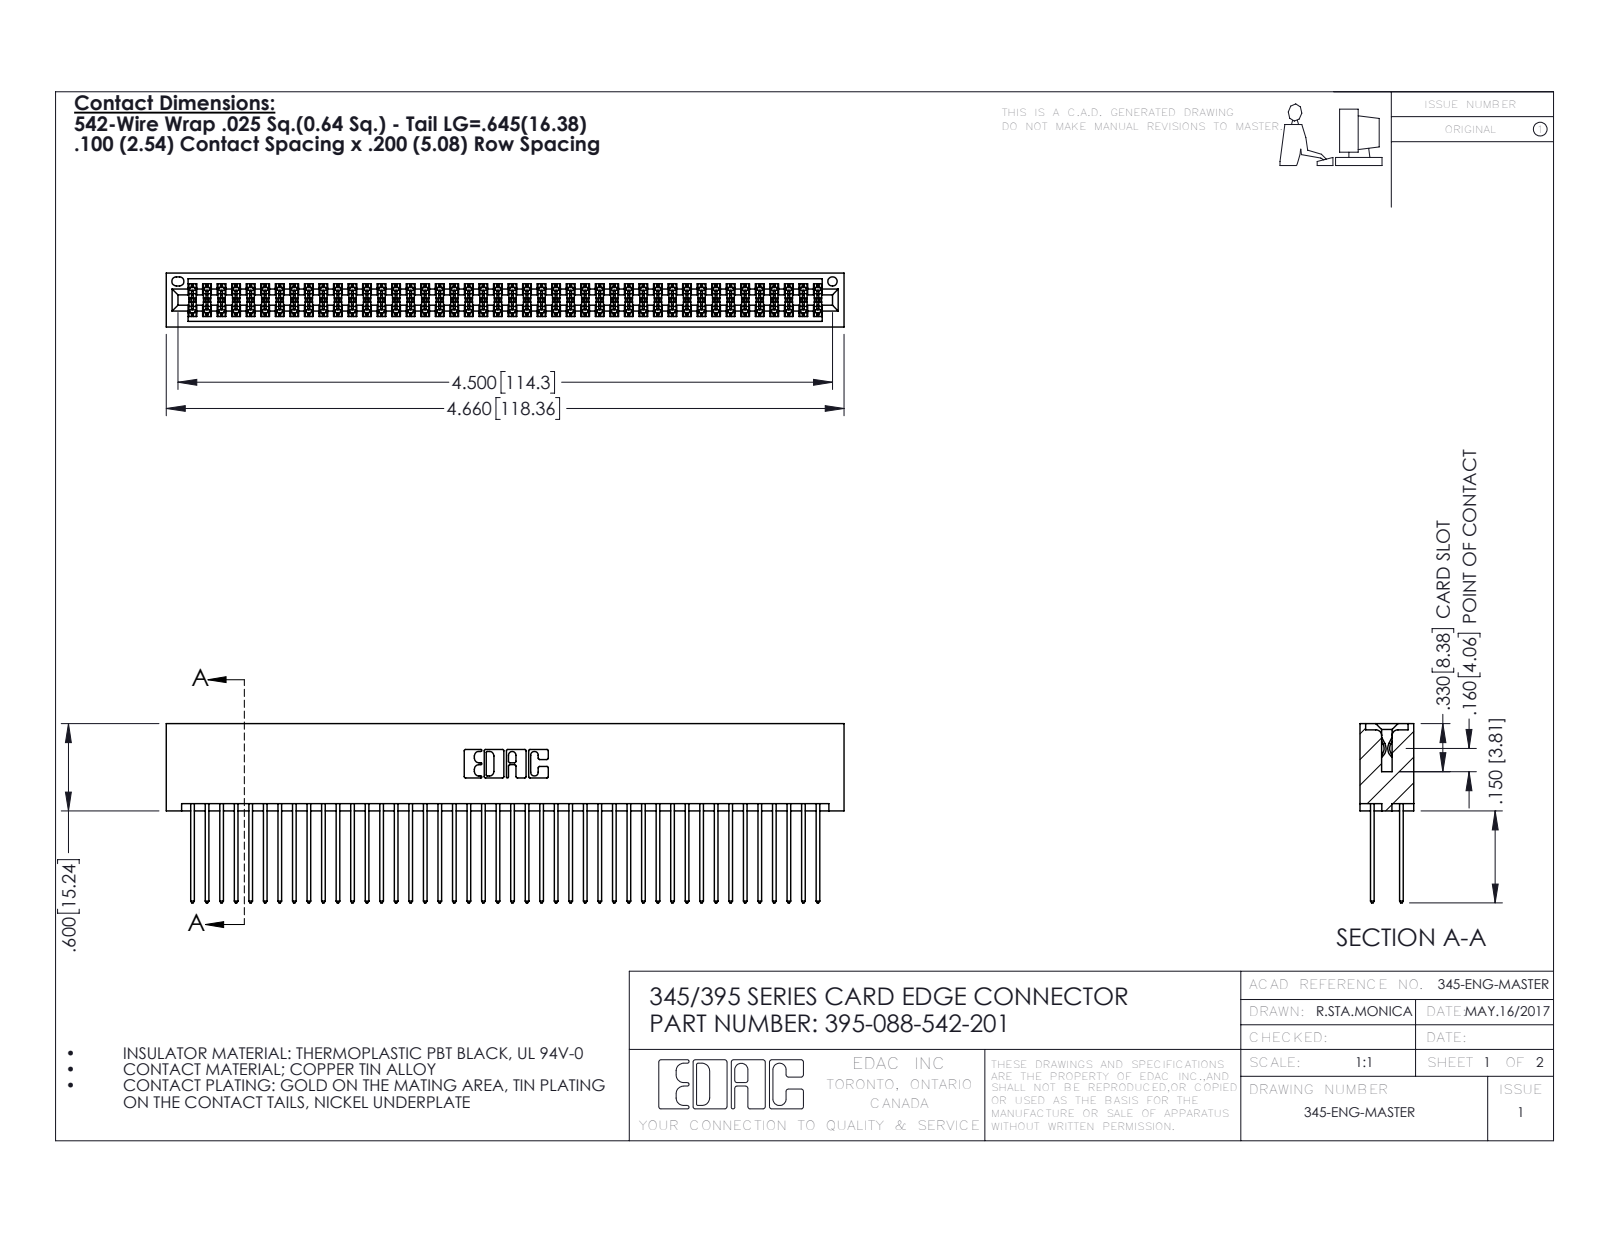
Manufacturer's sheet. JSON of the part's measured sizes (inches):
{"part_name": "345-292-001_345-293-142; 345 Part_No Mounting Lugs; 395-088-542-201", "step_written_by": "SolidWorks 2016 (CONFIG_CONTROL_DESIGN)", "units": "inches", "bodies": {"solids": 89, "faces": 4518, "planar": 2980, "cylindrical": 1538, "other": 0}, "overall_size": [4.66, 1.232, 0.37], "volume_in3": 0.765, "surface_area_in2": 32.24, "round_holes": [[0.064, 1]], "partial_cylinders_radius": [[0.006, 132], [0.01, 88], [0.01, 22], [0.007, 6], [0.031, 6], [0.026, 3], [0.014, 2], [0.019, 2]], "face_to_face_distances": [0.298, 0.072, 0.2, 0.098, 0.272, 0.025, 0.225, 0.37, 0.175, 0.149]}
